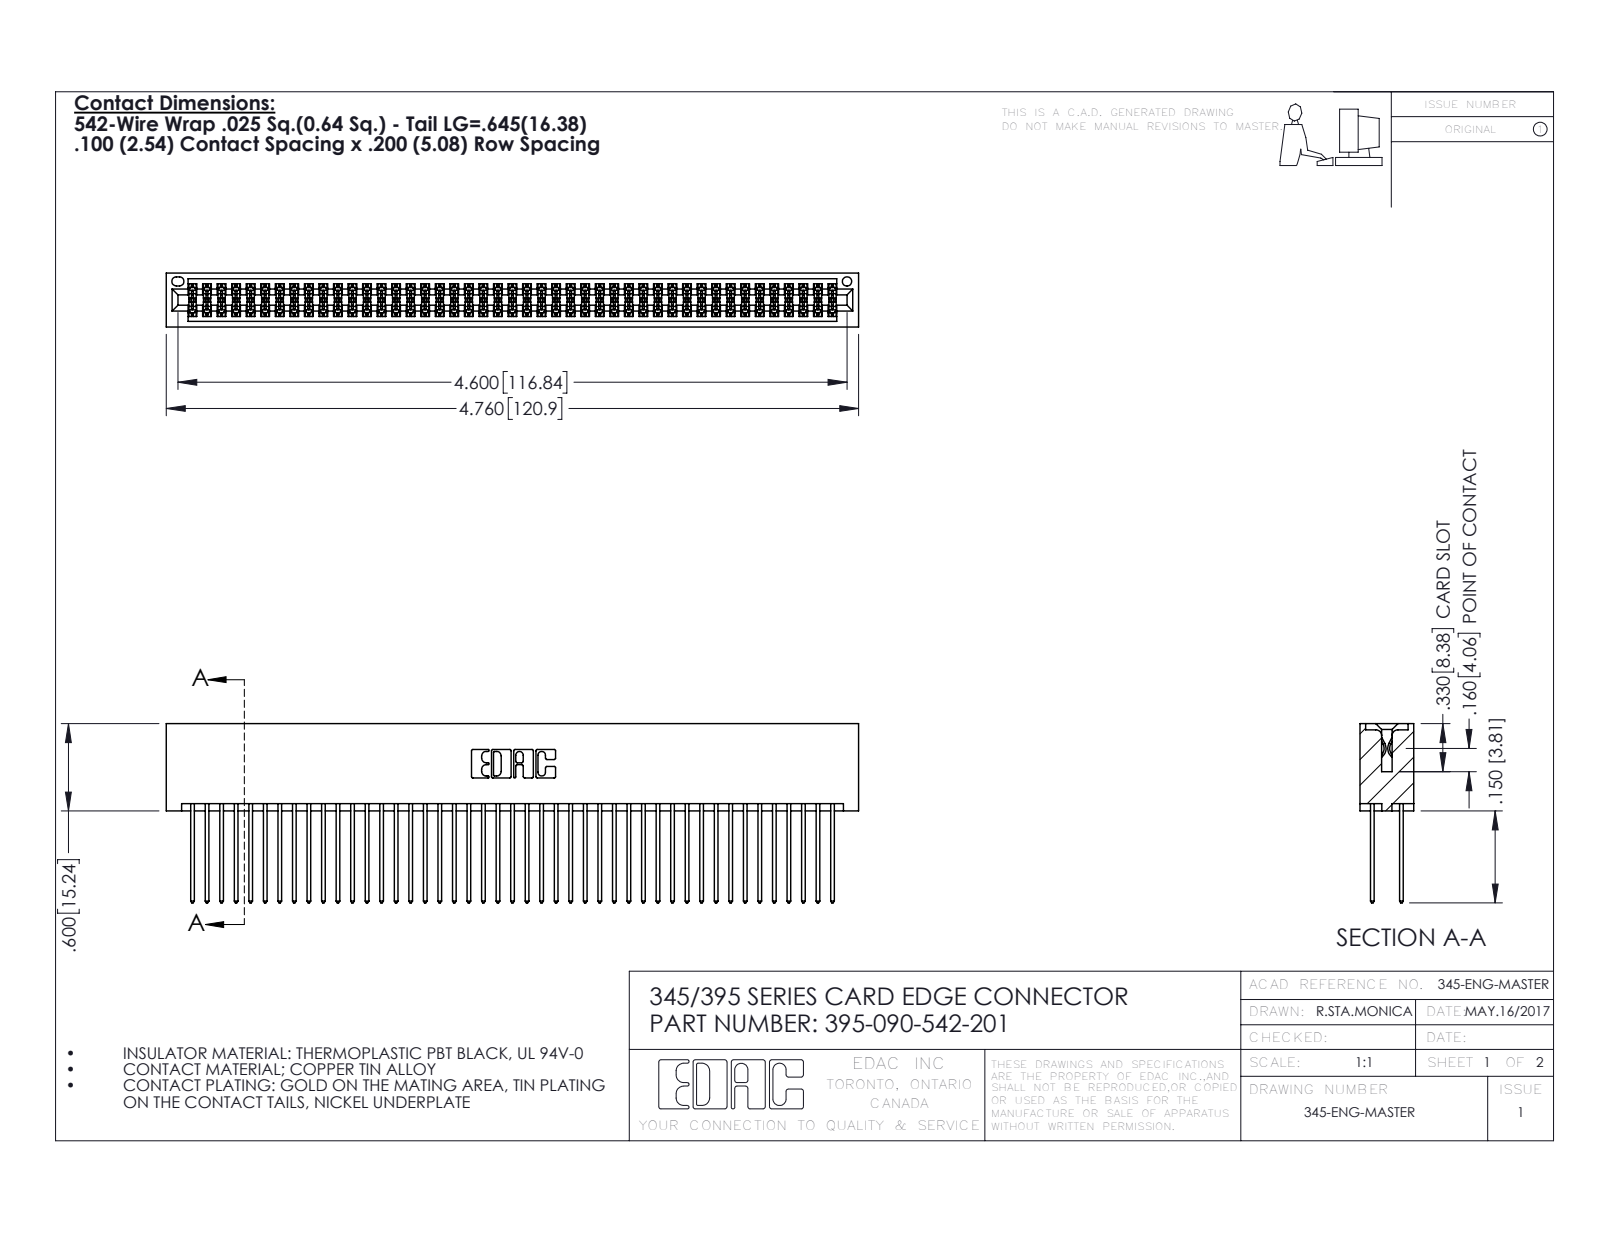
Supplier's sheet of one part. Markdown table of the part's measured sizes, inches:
| quantity | value |
| --- | --- |
| part name | 395-090-542-201; 345 Part_No Mounting Lugs; 345-292-001_345-293-142 |
| STEP written by | SolidWorks 2016 (CONFIG_CONTROL_DESIGN) |
| units | inches |
| bodies | 91 solids, 4618 faces (3046 planar, 1572 cylindrical, 0 other) |
| overall size | 4.76 × 1.232 × 0.37 |
| volume | 0.782 in³ |
| surface area | 32.94 in² |
| round holes (diameter × count) | 0.064 × 1 |
| partial cylindrical surfaces (radius × count) | 0.006 × 135, 0.01 × 90, 0.01 × 22, 0.007 × 6, 0.031 × 6, 0.026 × 3, 0.014 × 2, 0.019 × 2 |
| main face-to-face distances | 0.298, 0.072, 0.2, 0.098, 0.272, 0.025, 0.225, 0.37, 0.175, 0.149 |
